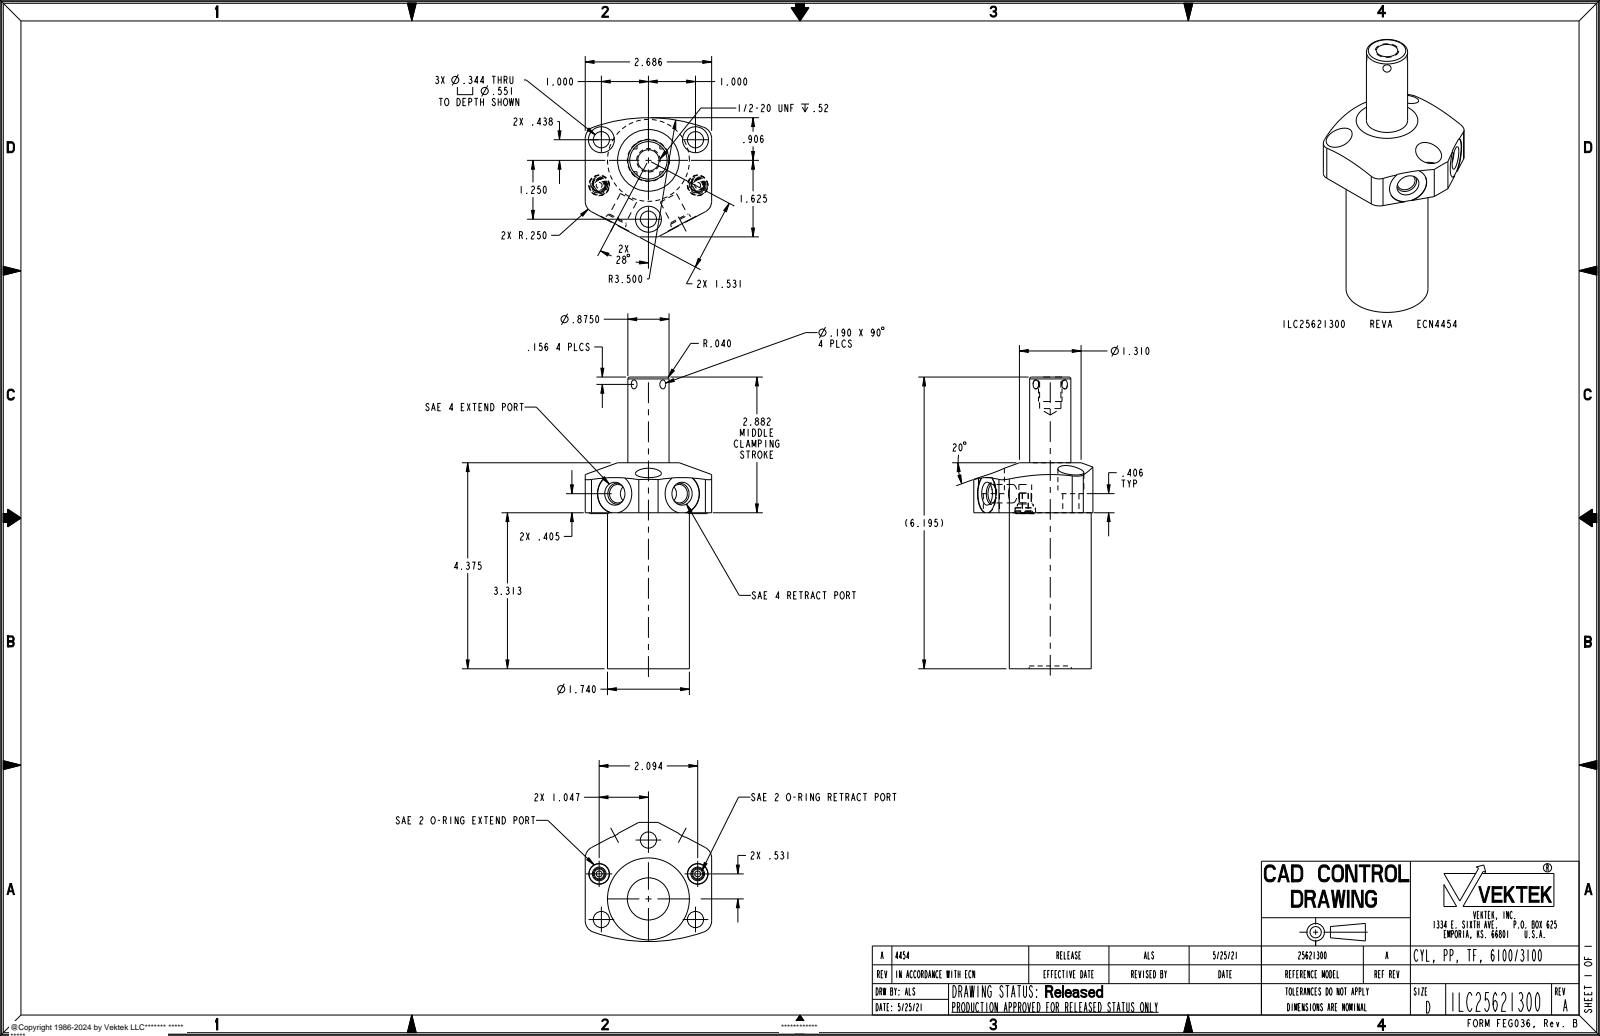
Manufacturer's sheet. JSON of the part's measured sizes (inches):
{"part_name": "ILC25621300", "step_written_by": "PRO/ENGINEER BY PARAMETRIC TECHNOLOGY CORPORATION, 2013320 (CONFIG_CONTROL_DESIGN)", "units": "inches", "bodies": {"solids": 1, "faces": 131, "planar": 34, "cylindrical": 59, "other": 38}, "overall_size": [6.195, 2.686, 2.531], "volume_in3": 13.64, "surface_area_in2": 51.61, "round_holes": [[0.344, 3], [0.551, 3], [0.125, 2], [0.272, 2], [0.392, 2], [0.438, 2], [0.453, 1], [0.895, 1]], "round_bosses_or_shafts": [[0.43, 2], [0.256, 2], [0.21, 2], [1.74, 1], [0.875, 1], [0.5, 1]], "partial_cylinders_radius": [[0.25, 4], [0.412, 2], [3.5, 1]], "face_to_face_distances": [3.313, 2.686, 4.375, 1.062, 0.06, 3.253, 4.315, 3.719, 3.659, 0.406], "hole_center_spacings": [0.97, 1.092, 1.174, 1.27, 1.962, 2.265, 1.25, 2]}
